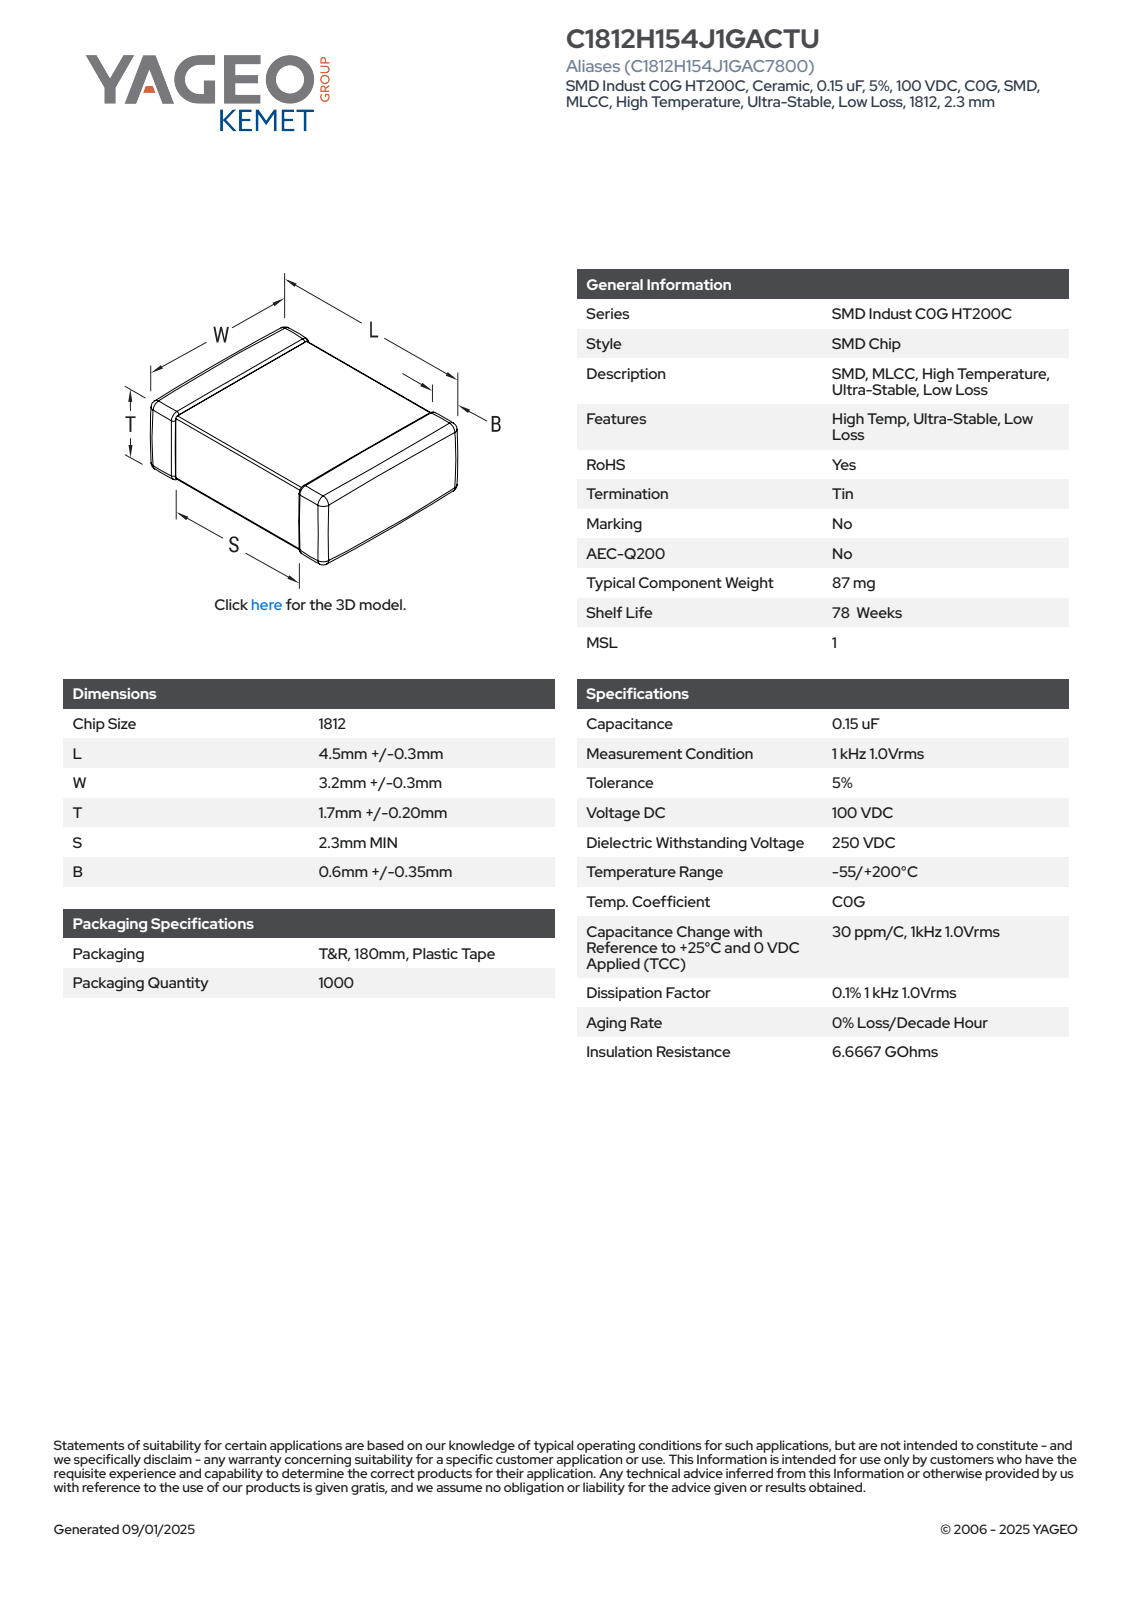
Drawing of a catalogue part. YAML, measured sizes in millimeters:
part_name: "CCS_CCSTDNOS_1812_L4.8W3.5T1.9B0.95"
step_written_by: "SolidWorks 2014 (AUTOMOTIVE_DESIGN)"
units: millimeters
bodies: {solids: 4, faces: 121, planar: 71, cylindrical: 34, other: 16}
overall_size: [4.8, 3.5, 1.9]
volume: 30
surface_area: 64
face_to_face_distances: [1.83, 1.76, 4.8, 3.43, 1.9, 3.36, 3.5, 1.49, 0.34, 1.94]
